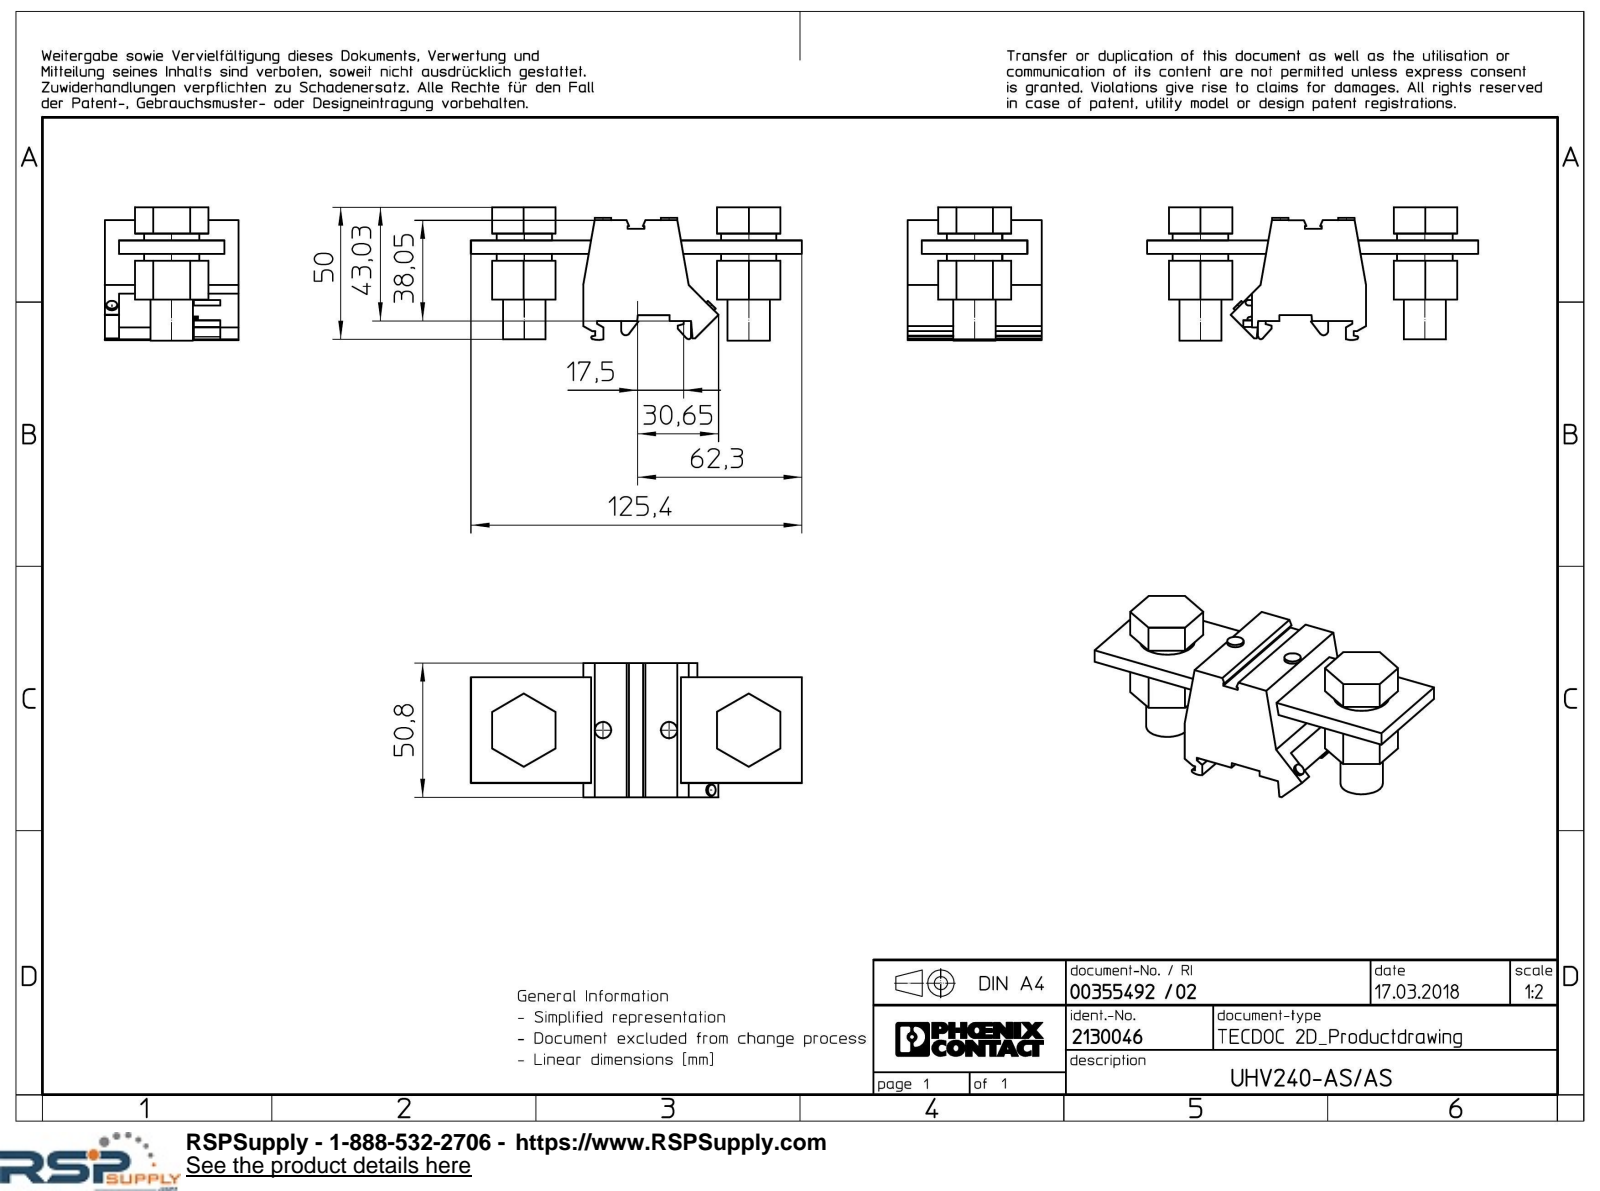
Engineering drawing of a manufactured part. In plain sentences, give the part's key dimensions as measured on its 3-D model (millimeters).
The part is named "UHV_240_AS_AS_select". Its 3-D file was written by "Creo Elements/Direct Modeling 18.1I 14-Aug-2016 (C) Parametric Technology GmbH (AUTOMOTIVE_DESIGN)". It is 1 solid with 131 faces: 107 planar, 24 cylindrical and 0 other. Overall it measures 125.4 by 50.8 by 50.5 millimeters. Its volume is 127 318 cubic millimeters and its surface area 28 865 square millimeters. Round bosses or shafts: 2 of diameter 21, 2 of diameter 16, 2 of diameter 6.2, 1 of diameter 4.11. Partial cylindrical surfaces (rounded edges, fillets, slot ends): 2 of radius 1, 1 of radius 0.5, 1 of radius 0.63, 1 of radius 1.7, 1 of radius 7.2. The main face-to-face distances are 5, 24, 50.8, 12.63, 7.63, 25.42, 30.42, 38.05, 12.6, 43.02.
